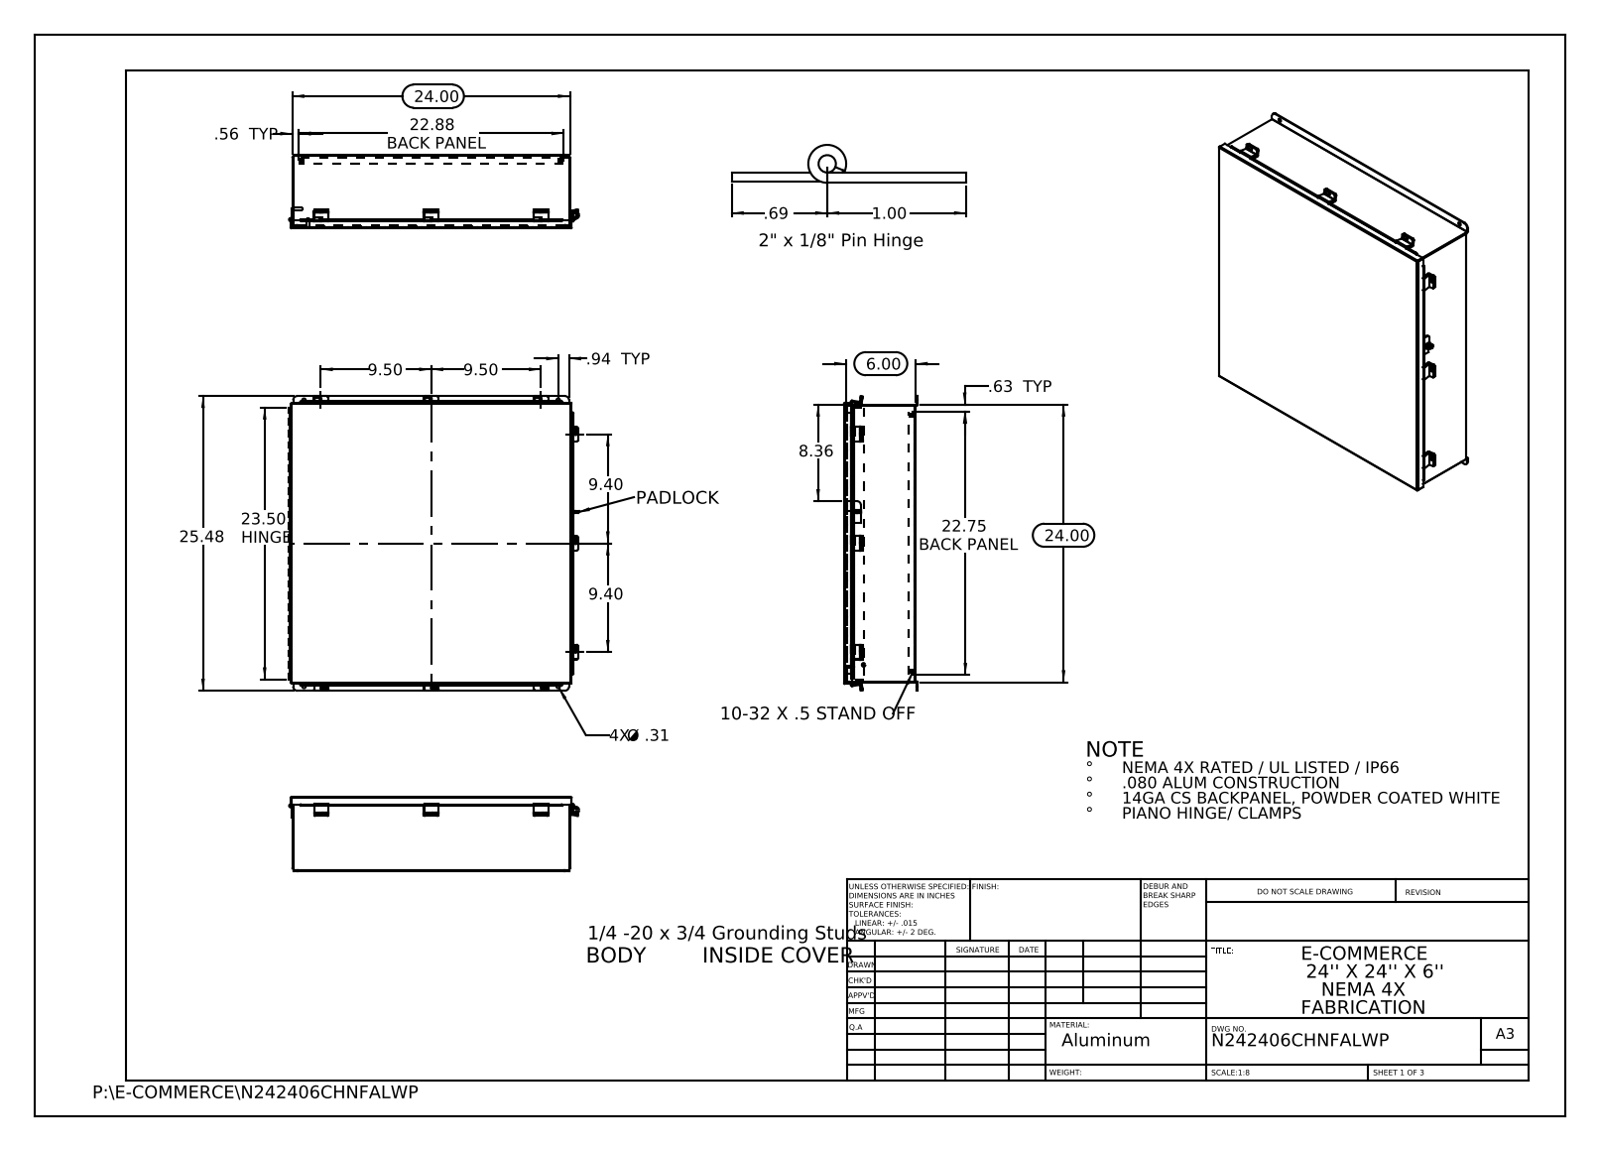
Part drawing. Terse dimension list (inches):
name: N242406CHNFALWP JIC_Cover_Template; N242406CHNFALWP JIC Bottom; N242406CHNFALWP JIC Clamp Bracket; N242406CHNFALWP JIC Backpanel (+8 more)
written by: SolidWorks 2013 (CONFIG_CONTROL_DESIGN)
unit: in
bodies: 33 solids, 1148 faces (715 planar, 413 cylindrical, 20 other)
size: 25.476 × 25.072 × 6.39
volume: 184.4 in³; area: 4 990 in²
holes: 13× ⌀0.25, 4× ⌀0.187, 4× ⌀0.312, 1× ⌀0.125, 1× ⌀0.125, 1× ⌀0.373, 1× ⌀0.375
bosses: 4× ⌀0.313, 2× ⌀0.315, 2× ⌀0.236, 1× ⌀0.273, 1× ⌀0.25
rounds: 31× R0.125, 18× R0.133, 13× R0.013, 12× R0.009, 12× R0.088, 6× R0.083, 6× R0.1, 4× R0.375
face distances: 0.075, 6.128, 23.925, 6.053, 6.203, 0.074, 5.628, 0.575, 0.5, 5.553
hole spacings: 1.315, 9.5, 22.213, 23.427, 32.257, 9.425, 19, 21.976
